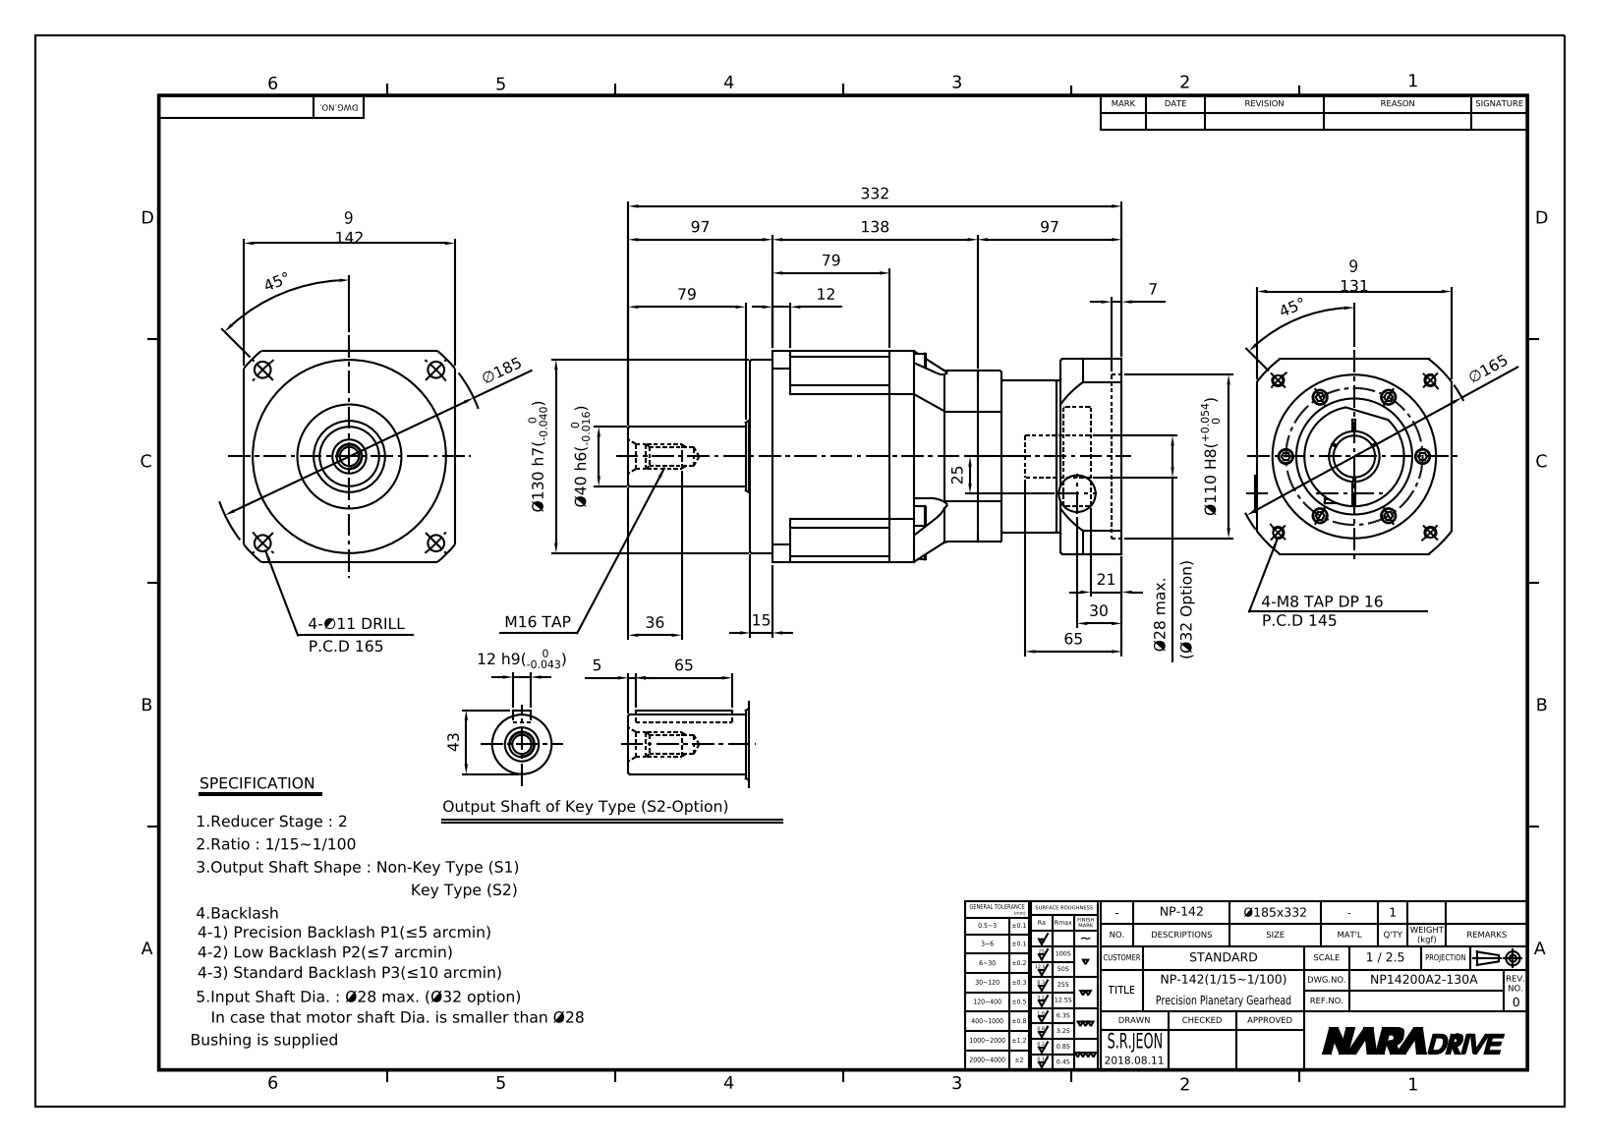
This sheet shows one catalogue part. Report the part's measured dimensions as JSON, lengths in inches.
{"part_name": "NP14200A2-130A-S1", "step_written_by": "Autodesk Inventor 2015 (AUTOMOTIVE_DESIGN)", "units": "inches", "bodies": {"solids": 2, "faces": 546, "planar": 249, "cylindrical": 156, "other": 141}, "overall_size": [13.071, 5.591, 5.591], "volume_in3": 169, "surface_area_in2": 445.9, "round_holes": [[0.433, 14], [0.194, 10], [0.26, 10], [0.262, 9], [0.335, 4], [0.354, 1], [0.492, 1], [0.545, 1], [0.571, 1], [0.669, 1], [1.102, 1], [1.339, 1]], "round_bosses_or_shafts": [[0.394, 10], [0.236, 10], [0.512, 5], [0.315, 5], [5.118, 1], [4.016, 1], [2.638, 1], [1.89, 1]], "partial_cylinders_radius": [[0.039, 12], [0.197, 8], [0.591, 8], [0.02, 4], [0.276, 1], [2.549, 1], [3.248, 1], [3.642, 1]], "face_to_face_distances": [5.591, 0.217, 5.374, 4.528, 3.346, 0.315, 0.531, 5.059, 4.843, 8.228], "hole_center_spacings": [1.811, 3.137, 3.666, 2.854, 4.037, 0.394, 2.029, 2.3]}
